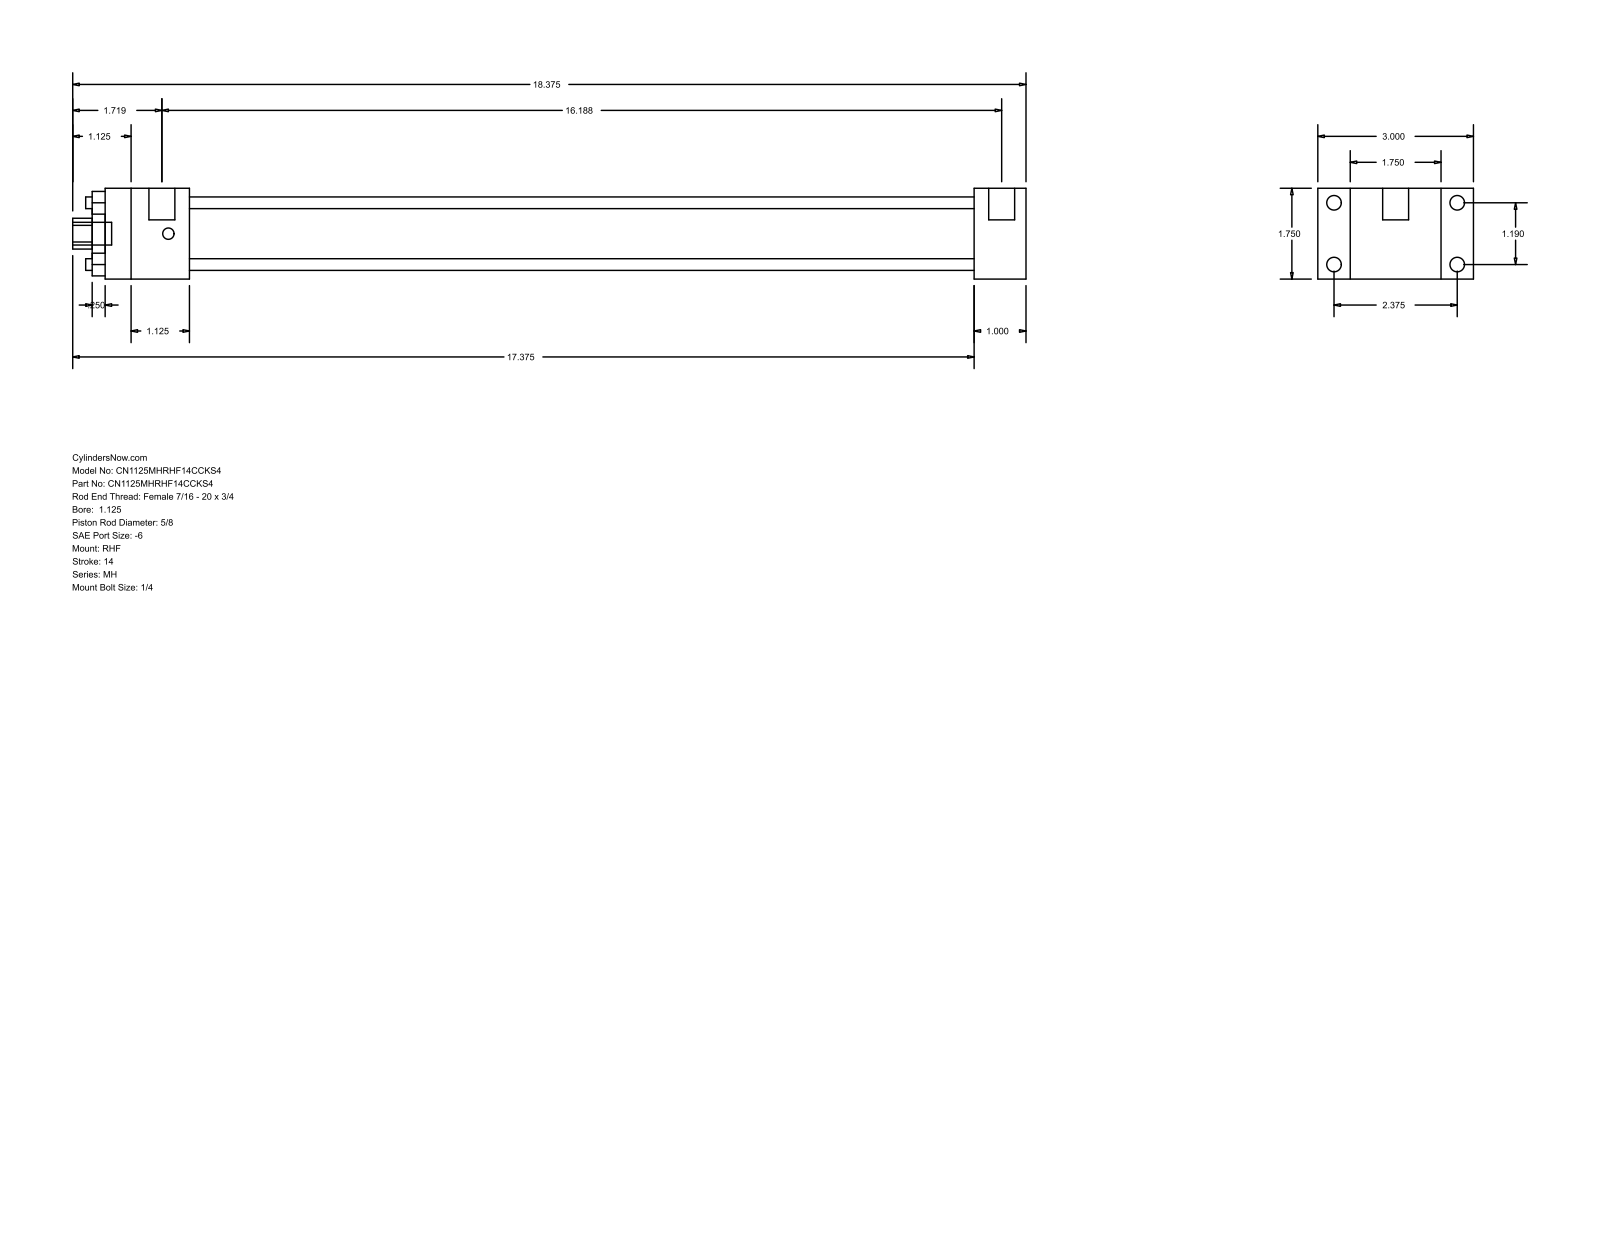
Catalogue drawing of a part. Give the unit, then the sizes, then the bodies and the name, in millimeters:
Units: millimetres
Overall size (bounding box): 466.73 × 76.2 × 44.45
Round holes (diameter × count): ⌀5.71 ×4, ⌀15.88 ×1, ⌀28.57 ×1, ⌀34.92 ×1
Round bosses / shafts (diameter × count): ⌀7.14 ×4, ⌀5.56 ×4, ⌀12.7 ×2, ⌀11.11 ×1
Partial cylindrical surfaces — rounded edges, fillets, slot ends (radius × count): R7.54 ×1
Main face-to-face distances: 44.46, 15.87, 60.33, 25.41, 76.2, 384.17, 409.58, 41.27, 425.44, 450.85
Hole centre spacings: 21.37, 30.22, 42.74
Bodies: 0 solids, 88 faces (60 planar, 28 cylindrical, 0 other)
Part name (STEP PRODUCT): MH_RHF__0112_0.625
STEP written by: GSSL Pune (CONFIG_CONTROL_DESIGN)
